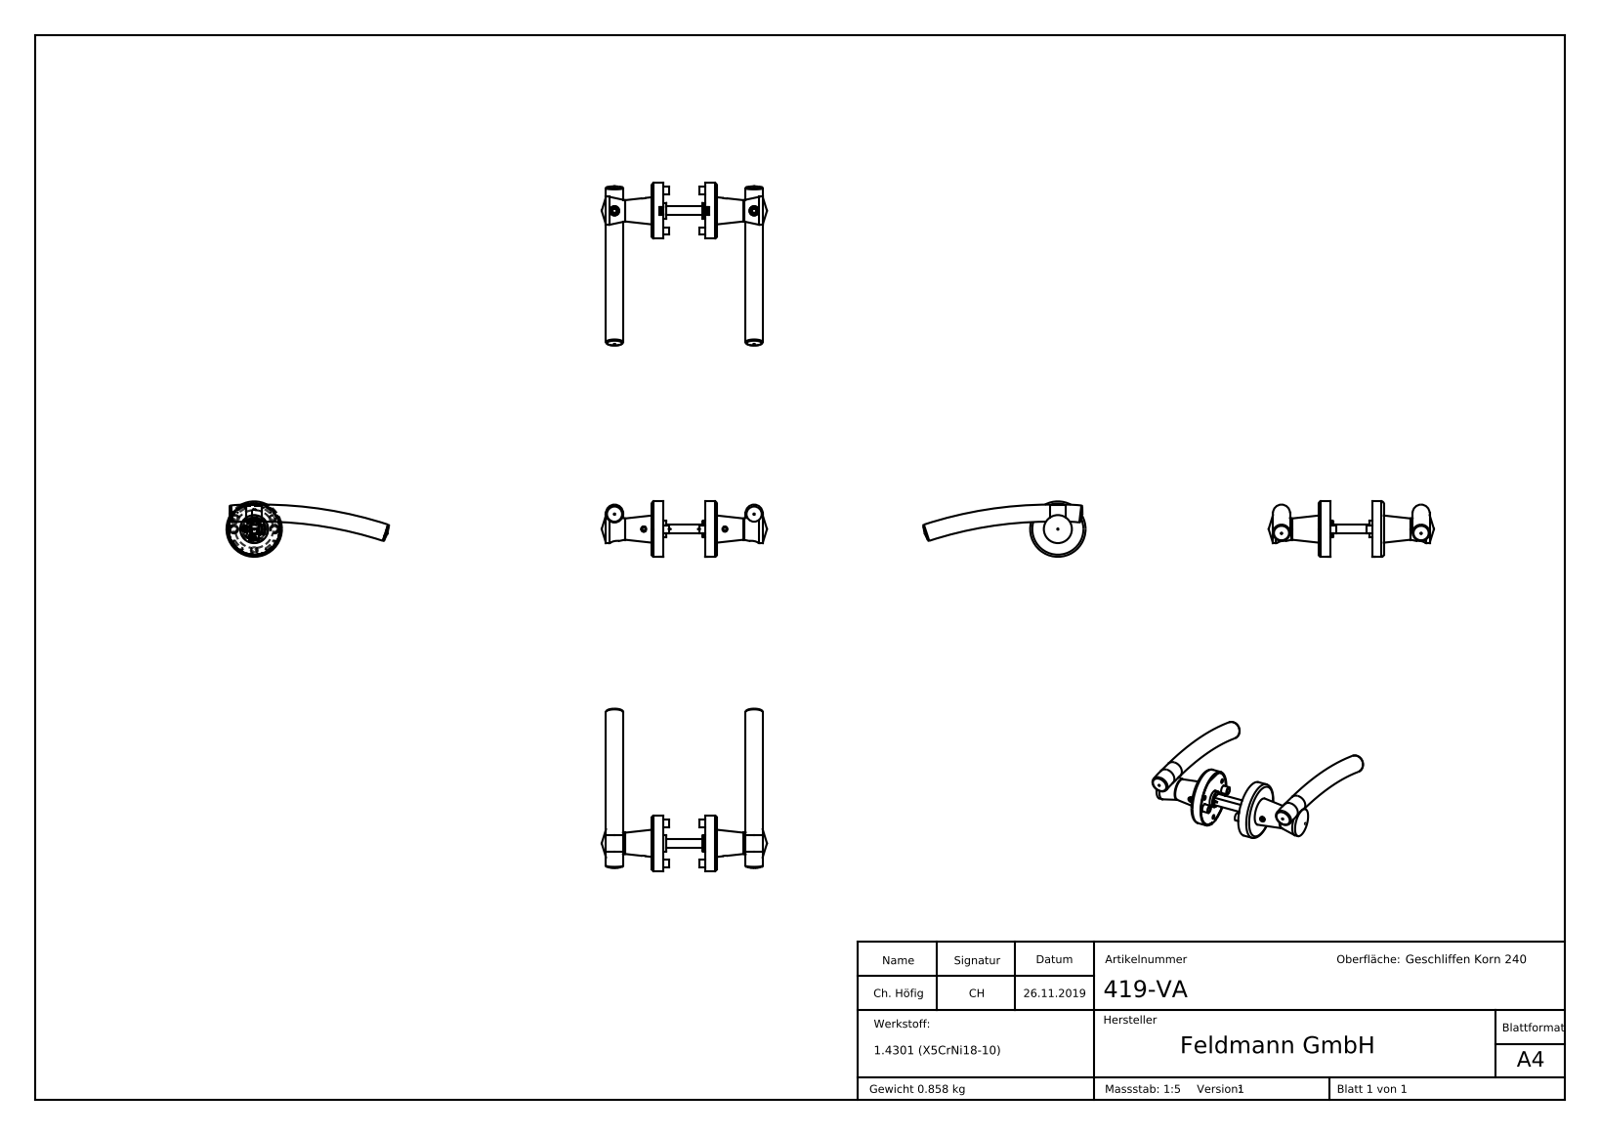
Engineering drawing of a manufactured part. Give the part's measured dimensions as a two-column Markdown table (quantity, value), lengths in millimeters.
| quantity | value |
| --- | --- |
| part name | 4XX-VA Teil3; DIN914; 4XX-VA Teil1_419-VA Teil5; DIN 912 - M5x16_DIN 912 M5x16 (+8 more) |
| STEP written by | SolidWorks 2015 (CONFIG_CONTROL_DESIGN) |
| units | millimeters |
| bodies | 18 solids, 952 faces (539 planar, 137 cylindrical, 276 other) |
| overall size | 70000 × 19994.71 × 5999.86 |
| volume | 179 268 mm³ |
| surface area | 83 675 mm² |
| round holes (diameter × count) | 5.5 × 5, 3.7 × 3, 4.2 × 3, 5 × 3, 6.1 × 3, 8.9 × 3, 16 × 3, 7.3 × 2, 8 × 2, 15.4 × 1, 15.7 × 1, 16.2 × 1 |
| round bosses / shafts (diameter × count) | 8.5 × 2, 7.1 × 2, 6 × 2, 5 × 2, 52 × 1, 50 × 1, 49.8 × 1, 26.3 × 1 |
| partial cylindrical surfaces (radius × count) | 1 × 4, 4.5 × 1, 17.85 × 1, 21 × 1, 23 × 1 |
| main face-to-face distances | 10.5, 50.5, 1, 60, 9.5, 49.5, 8.1, 40, 61, 8 |
| hole center spacings | 20, 31.32, 34.64, 46, 10.14, 19, 27.59, 37.67 |
